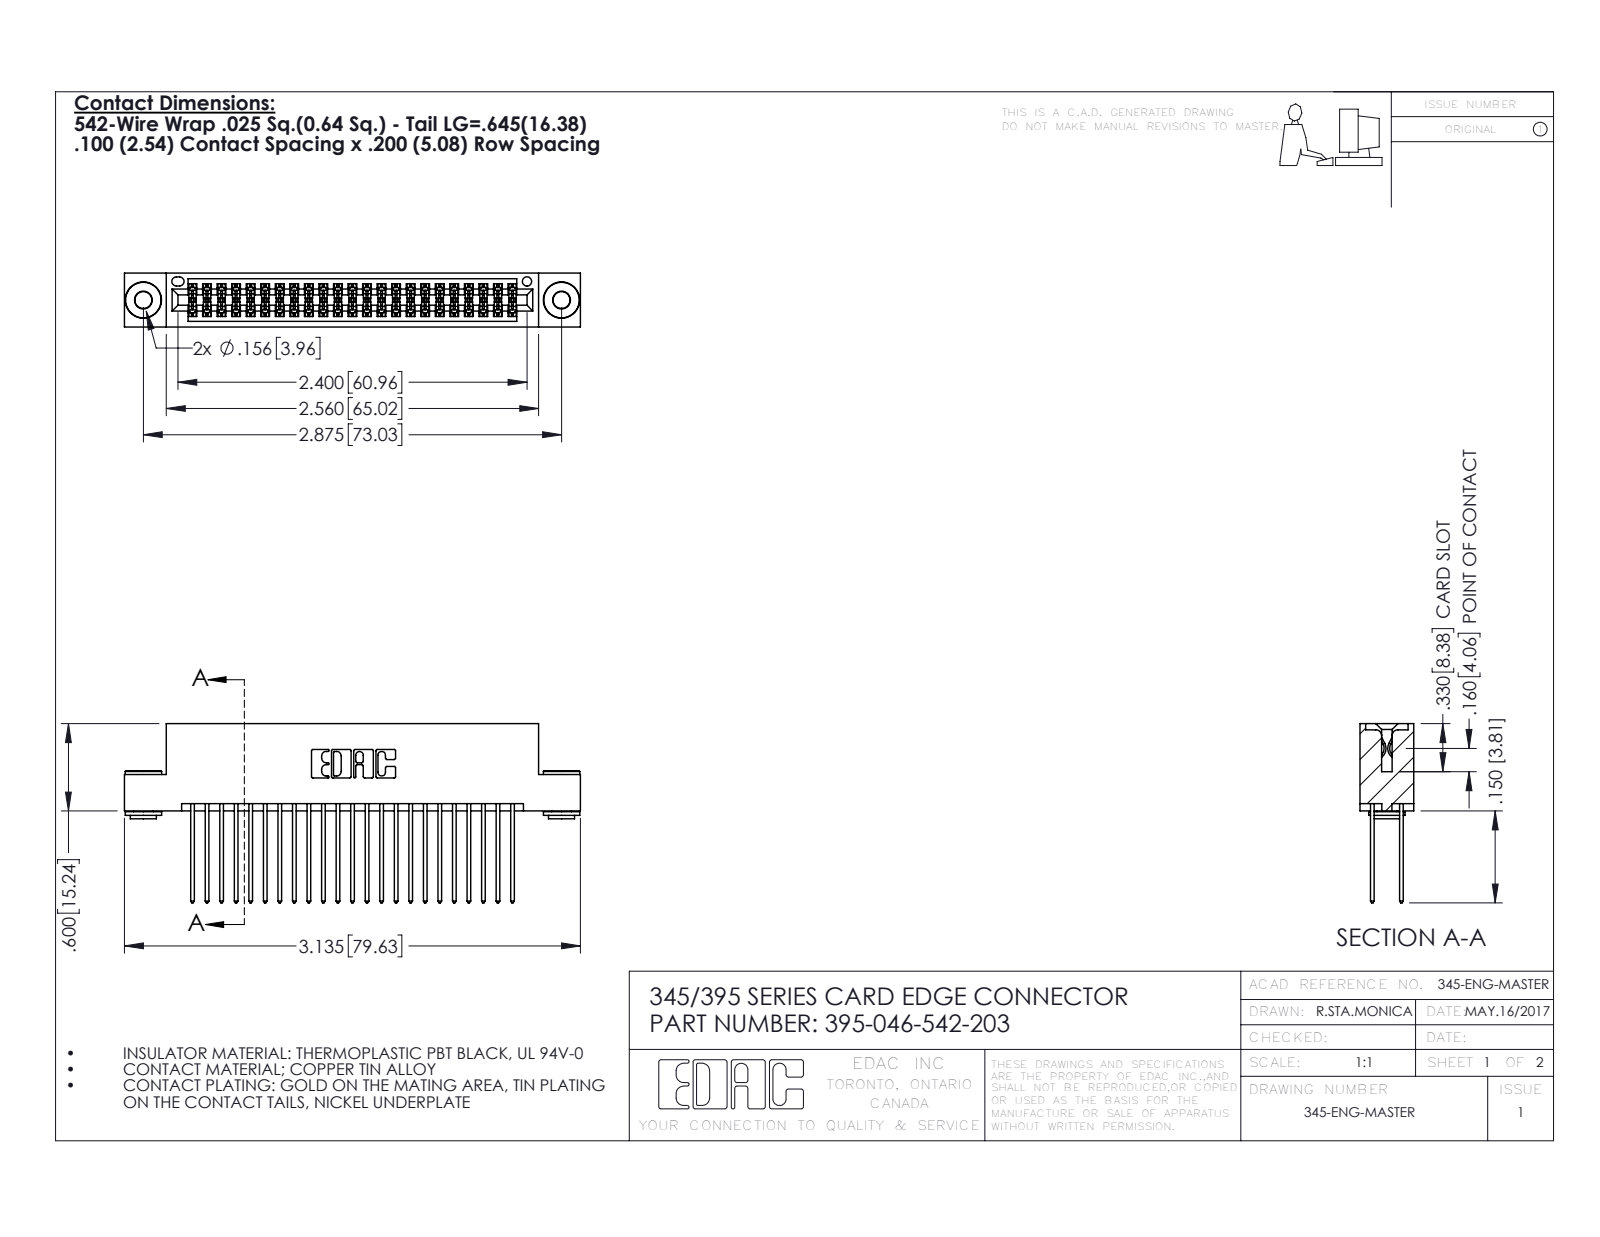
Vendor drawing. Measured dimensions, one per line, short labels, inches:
name: 345 Part_Flush Mounting Lugs - 0.156 Dia-TH; 345-292-001_345-293-142; 345-250-002_345-250-002-102; 395-046-542-203
written by: SolidWorks 2016 (CONFIG_CONTROL_DESIGN)
unit: in
bodies: 49 solids, 2464 faces (1608 planar, 848 cylindrical, 8 other)
size: 3.135 × 1.232 × 0.37
volume: 0.476 in³; area: 19.15 in²
holes: 2× ⌀0.116, 2× ⌀0.156, 1× ⌀0.064
bosses: 2× ⌀0.25, 2× ⌀0.18, 2× ⌀0.136
rounds: 69× R0.006, 46× R0.01, 22× R0.01, 6× R0.007, 6× R0.031, 3× R0.026, 2× R0.014, 2× R0.019
face distances: 0.072, 0.298, 0.2, 0.025, 0.098, 0.272, 0.37, 0.225, 0.175, 0.149
hole spacings: 0.27, 2.641, 2.875
